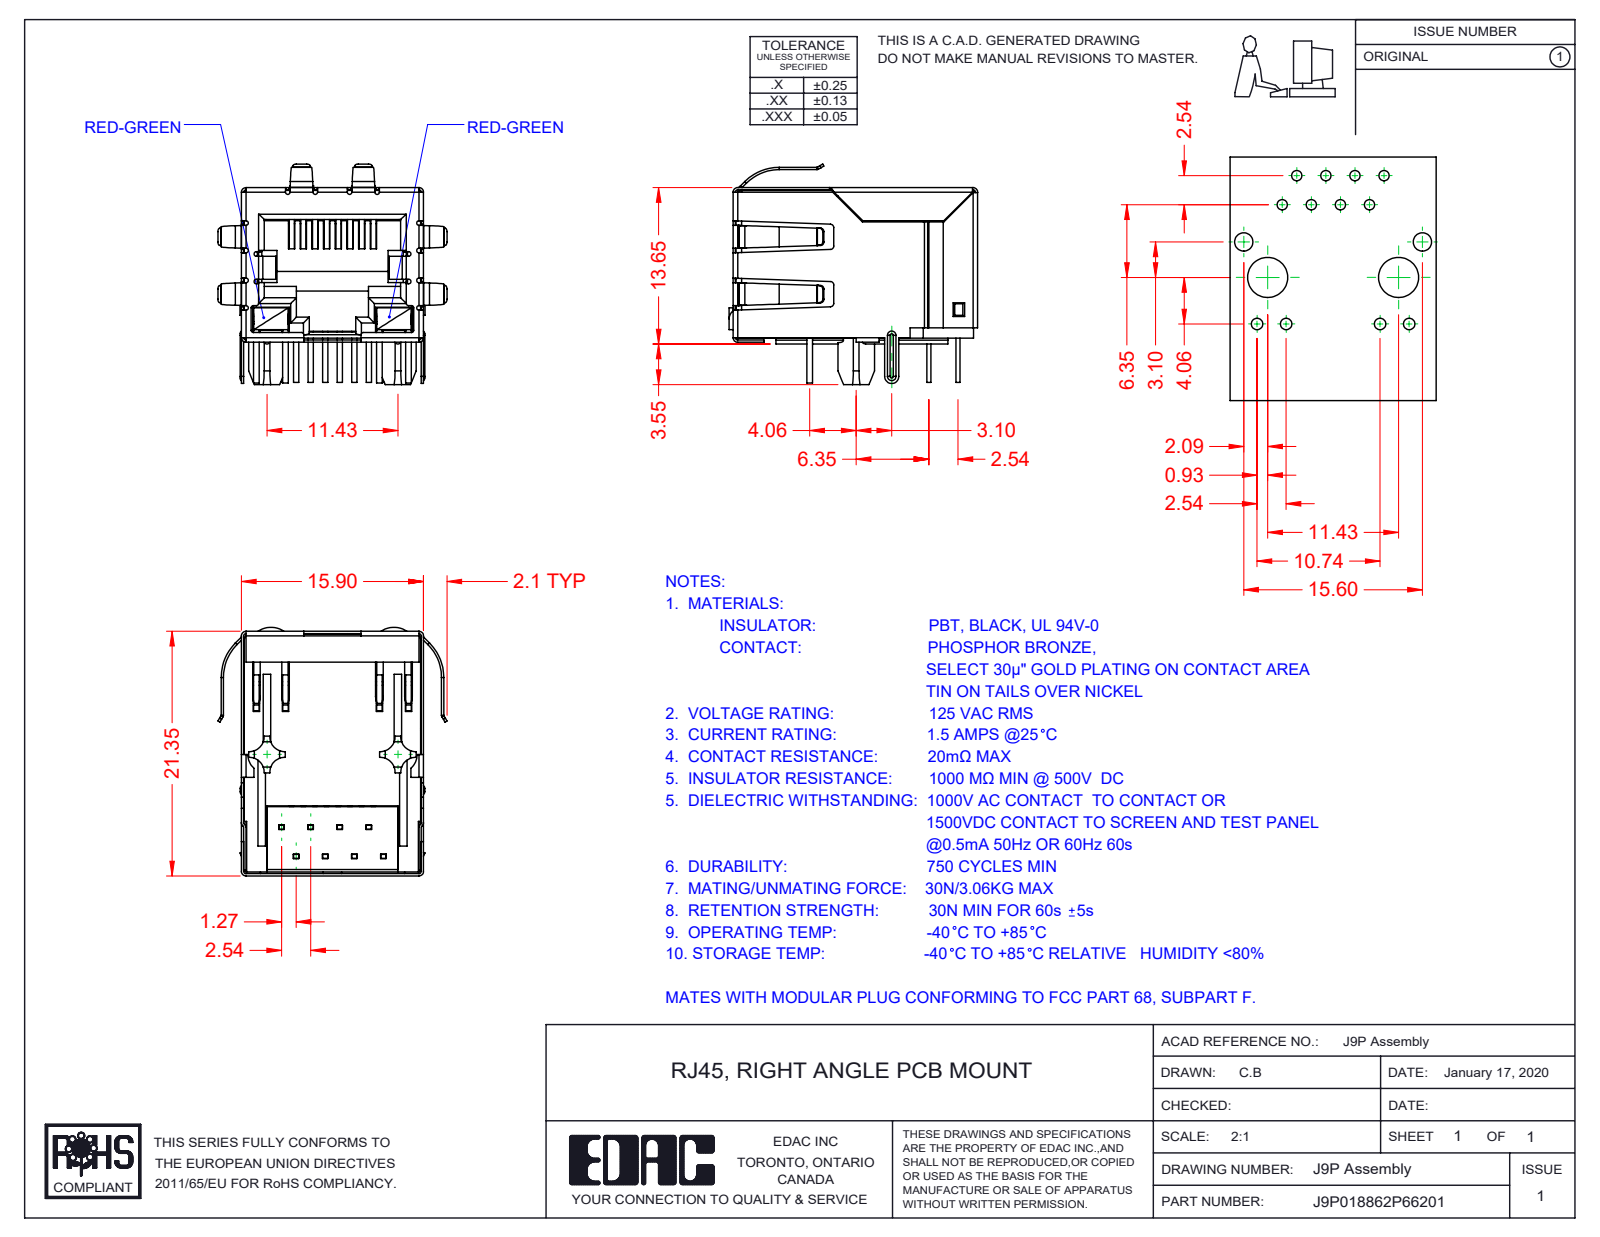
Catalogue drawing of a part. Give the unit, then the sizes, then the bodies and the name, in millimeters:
Units: millimetres
Overall size (bounding box): 21.7 × 20 × 19.25
Partial cylindrical surfaces — rounded edges, fillets, slot ends (radius × count): R0.2 ×39, R0.5 ×22, R0.3 ×20, R0.4 ×16, R1.3 ×8, R0.23 ×5, R0.11 ×4, R0.31 ×4
Main face-to-face distances: 15.45, 15.7, 15.65, 0.35, 0.54, 15.5, 12.36, 0.6, 1.4, 0.59
Volume: 2 687 mm³ · Surface area: 7 515 mm²
Bodies: 13 solids, 1476 faces (1042 planar, 340 cylindrical, 94 other)
Part name (STEP PRODUCT): 9P-LED LED RH_6-Red-Green; 9P-LED Contact Lock; 9P-LED Insulator; 9P-LED Contacts (+4 more)
STEP written by: SolidWorks 2016 (CONFIG_CONTROL_DESIGN)
